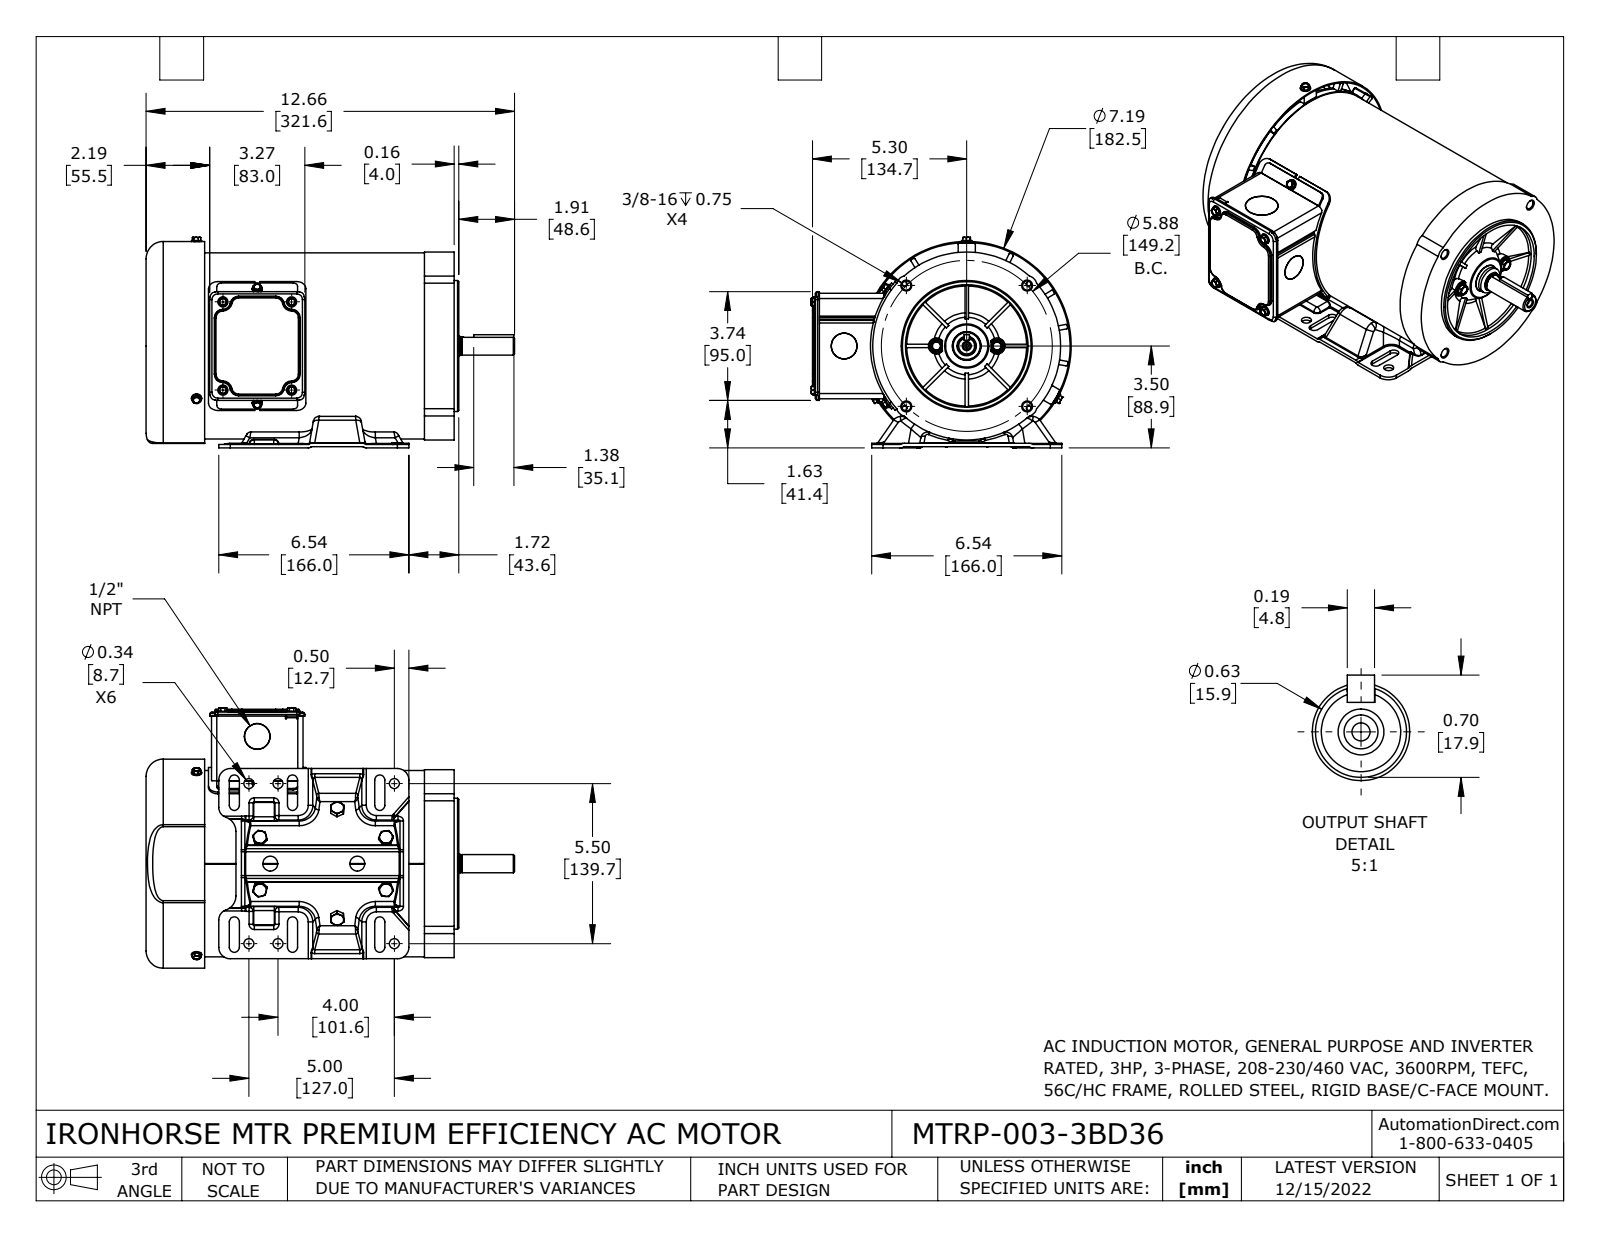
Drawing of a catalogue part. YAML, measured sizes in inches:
part_name: "MTRP-003-3BD36"
step_written_by: "SolidWorks 2021 (CONFIG_CONTROL_DESIGN)"
units: inches
bodies: {solids: 43, faces: 3590, planar: 843, cylindrical: 1153, other: 1594}
overall_size: [12.661, 8.938, 7.234]
volume: 46.9
surface_area: 1000
round_holes:
  - {diameter: 0.197, count: 12}
  - {diameter: 0.219, count: 9}
  - {diameter: 0.273, count: 7}
  - {diameter: 0.217, count: 6}
  - {diameter: 0.276, count: 6}
  - {diameter: 0.344, count: 6}
  - {diameter: 0.136, count: 5}
  - {diameter: 0.15, count: 4}
  - {diameter: 0.177, count: 4}
  - {diameter: 0.313, count: 4}
  - {diameter: 0.067, count: 2}
  - {diameter: 0.134, count: 2}
round_bosses_or_shafts:
  - {diameter: 0.164, count: 9}
  - {diameter: 0.414, count: 7}
  - {diameter: 0.19, count: 7}
  - {diameter: 0.348, count: 6}
  - {diameter: 0.25, count: 6}
  - {diameter: 0.348, count: 3}
  - {diameter: 7.185, count: 1}
  - {diameter: 6.457, count: 1}
partial_cylinders:
  - {radius: 0.02, count: 204}
  - {radius: 0.118, count: 123}
  - {radius: 0.079, count: 43}
  - {radius: 0.157, count: 32}
  - {radius: 0.039, count: 30}
  - {radius: 0.138, count: 26}
  - {radius: 0.276, count: 19}
  - {radius: 0.197, count: 13}
face_to_face_distances: [0.118, 0.039, 0.063, 0.157, 10.591, 10.551, 0.079, 3.559, 3.087, 0.047]
hole_center_spacings: [4.221, 3.031, 0.094, 2.32, 2.409, 2.937, 2.979, 3.748]
